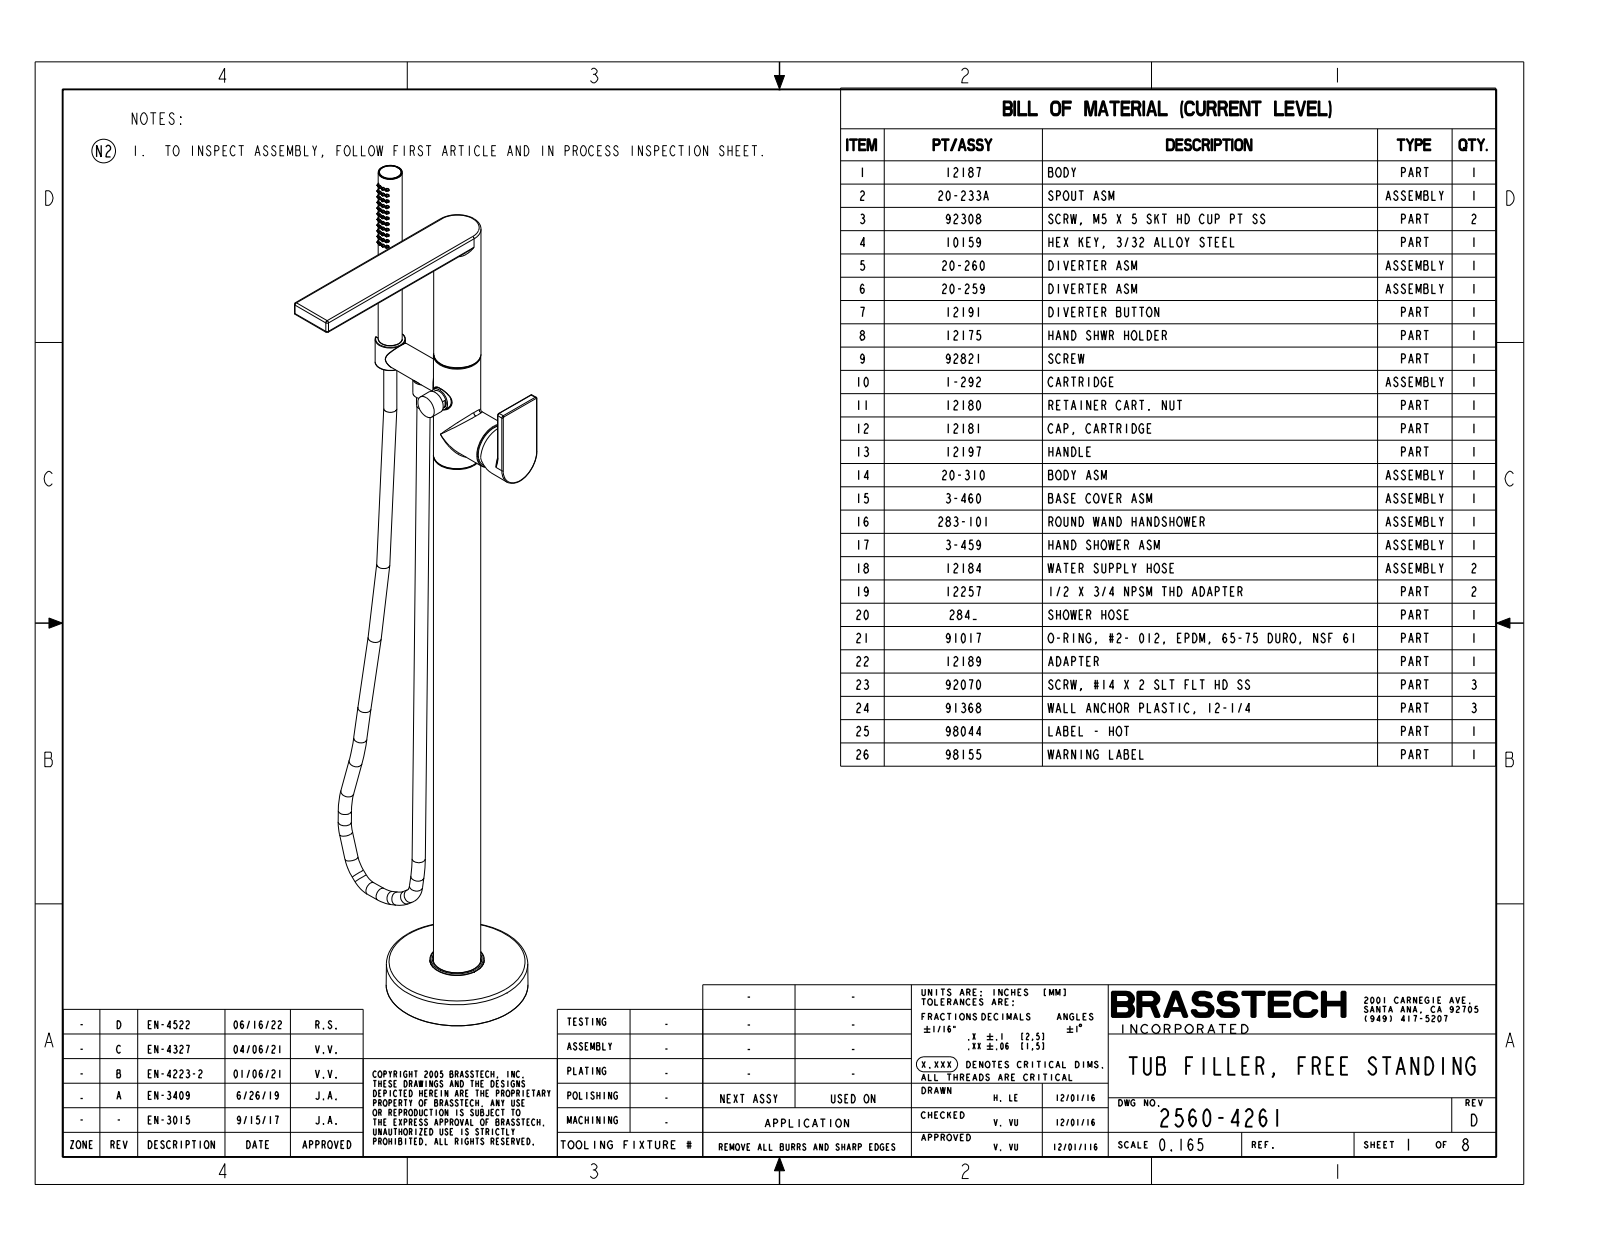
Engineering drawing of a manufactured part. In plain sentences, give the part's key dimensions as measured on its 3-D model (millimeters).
The part is named "2560-4261". Its 3-D file was written by "CREO PARAMETRIC BY PTC INC, 2018400 (AUTOMOTIVE_DESIGN)". It is 1 solid with 4162 faces: 1966 planar, 1418 cylindrical and 778 other. Overall it measures 1003.1 by 294.5 by 269.4 millimeters. Its volume is 2 966 000 cubic millimeters and its surface area 387 400 square millimeters. Round holes: 552 of diameter 0.5, 44 of diameter 3.6, 1 of diameter 5, 1 of diameter 5.5, 1 of diameter 7.8, 1 of diameter 8, 1 of diameter 16, 1 of diameter 18, 1 of diameter 23.9, 1 of diameter 24.5, 1 of diameter 50.5. Round bosses or shafts: 14 of diameter 14, 3 of diameter 50, 2 of diameter 22.9, 1 of diameter 57.5, 1 of diameter 32, 1 of diameter 30, 1 of diameter 25.4, 1 of diameter 24.5. Partial cylindrical surfaces (rounded edges, fillets, slot ends): 10 of radius 2, 6 of radius 0.5, 4 of radius 1, 4 of radius 1.6, 4 of radius 2.5, 1 of radius 8.6, 1 of radius 9.3, 1 of radius 9.3. The main face-to-face distances are 2, 13, 981, 979, 968, 11, 15, 966, 48, 50. The hole center spacings are 8.5, 15.3, 4.3, 29.8, 22.5, 7.4, 11.4, 14.7.
